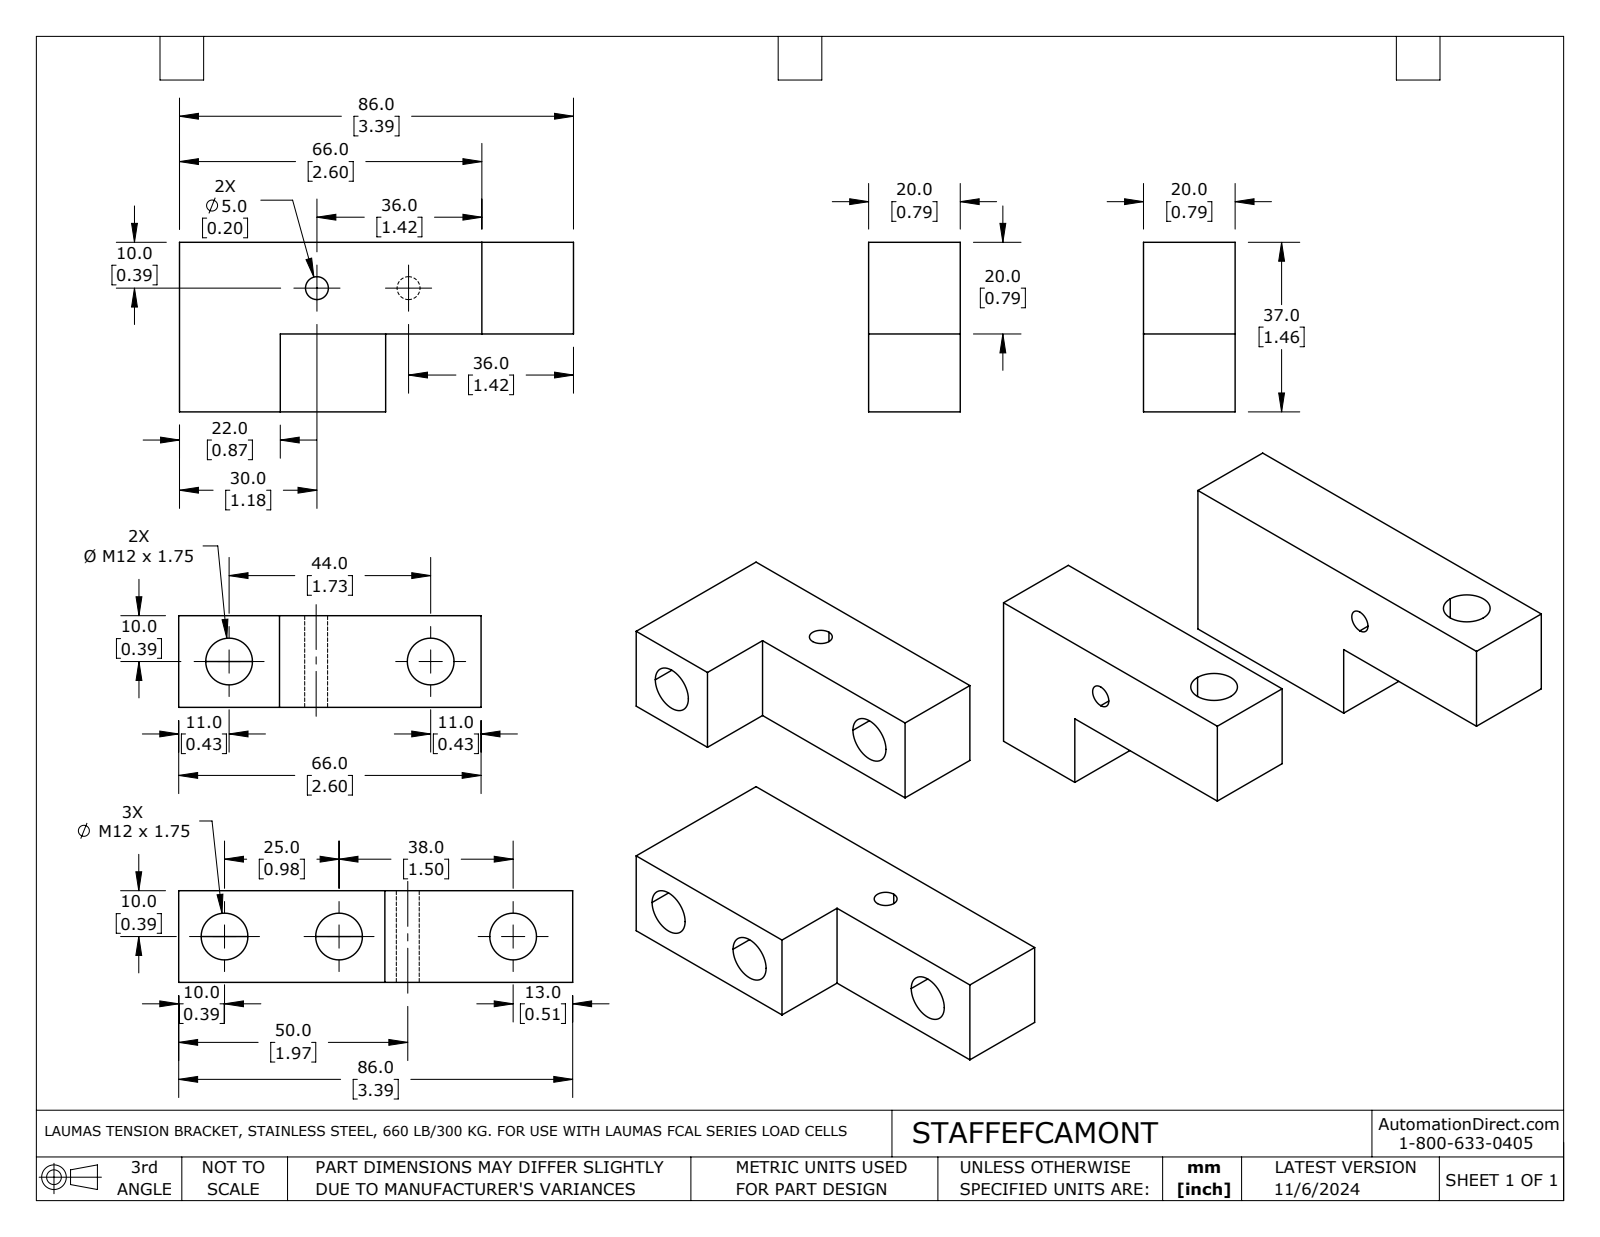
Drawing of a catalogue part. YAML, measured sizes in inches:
part_name: "STAFFEFCAMONT"
step_written_by: "SolidWorks 2021 (AUTOMOTIVE_DESIGN)"
units: inches
bodies: {solids: 3, faces: 49, planar: 19, cylindrical: 22, other: 8}
overall_size: [3.386, 3.15, 1.457]
volume: 4.677
surface_area: 33.86
round_holes:
  - {diameter: 0.402, count: 5}
  - {diameter: 0.197, count: 2}
round_bosses_or_shafts:
  - {diameter: 0.472, count: 1}
face_to_face_distances: [0.787, 2.362, 3.15, 1.575, 0.669, 1.457, 2.598, 3.386, 0.866, 1.772]
hole_center_spacings: [0.787, 0.984, 1.496, 1.732, 2.363, 2.466, 2.48, 2.49]
